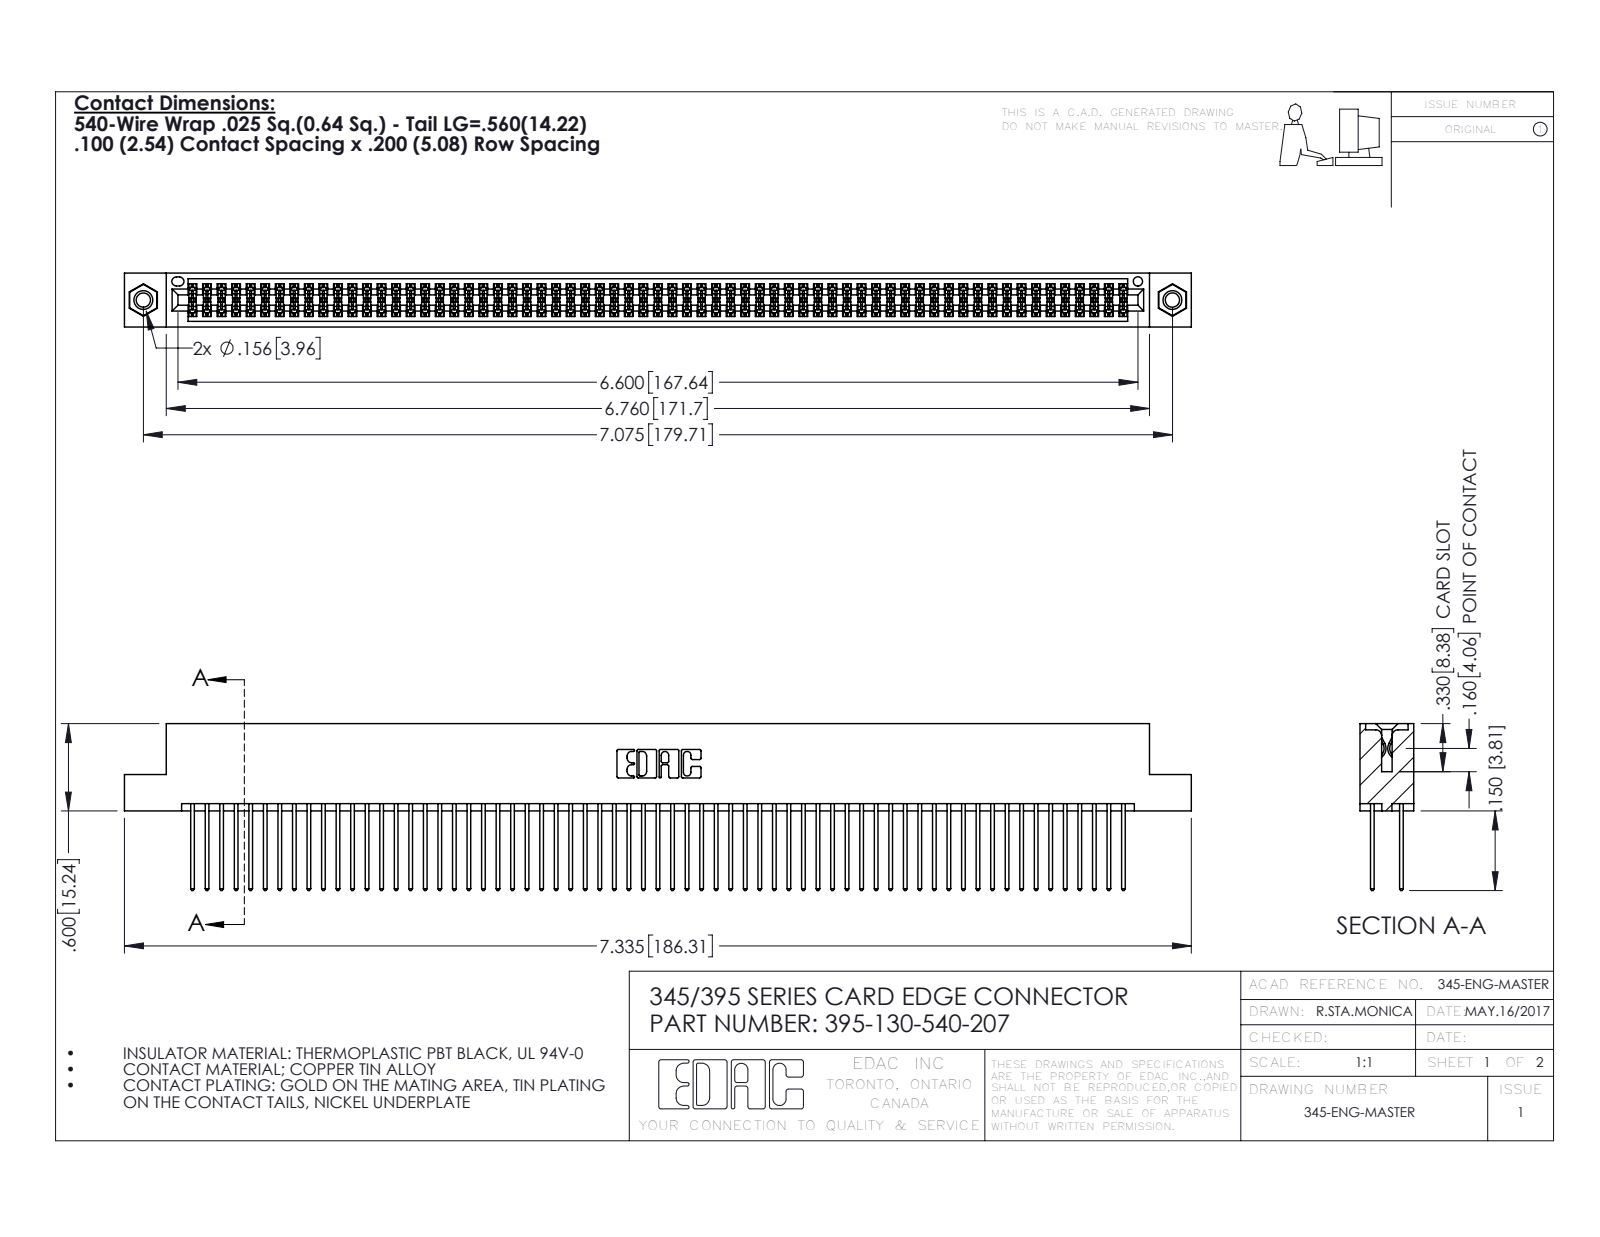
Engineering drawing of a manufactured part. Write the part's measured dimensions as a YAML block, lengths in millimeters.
part_name: "345-292-001_345-293-140; 395-130-540-207; 345 Part_Flush Mounting Lugs - 0.156 Dia-TI; 345-250-001_345-250-005-103"
step_written_by: "SolidWorks 2016 (CONFIG_CONTROL_DESIGN)"
units: millimeters
bodies: {solids: 133, faces: 6686, planar: 4402, cylindrical: 2268, other: 16}
overall_size: [186.3, 29.1, 9.4]
volume: 18800
surface_area: 30540
round_holes:
  - {diameter: 2.5, count: 2}
  - {diameter: 3.2, count: 2}
  - {diameter: 4, count: 2}
  - {diameter: 1.6, count: 1}
round_bosses_or_shafts:
  - {diameter: 3.9, count: 2}
partial_cylinders:
  - {radius: 0.2, count: 195}
  - {radius: 0.3, count: 130}
  - {radius: 0.3, count: 22}
  - {radius: 0.2, count: 6}
  - {radius: 0.8, count: 6}
  - {radius: 0.7, count: 3}
  - {radius: 0.4, count: 2}
  - {radius: 0.5, count: 2}
face_to_face_distances: [1.8, 7.6, 5.1, 2.5, 6.9, 0.6, 9.4, 5.7, 4.4, 3.8]
hole_center_spacings: [6.9, 173.7, 179.7]
